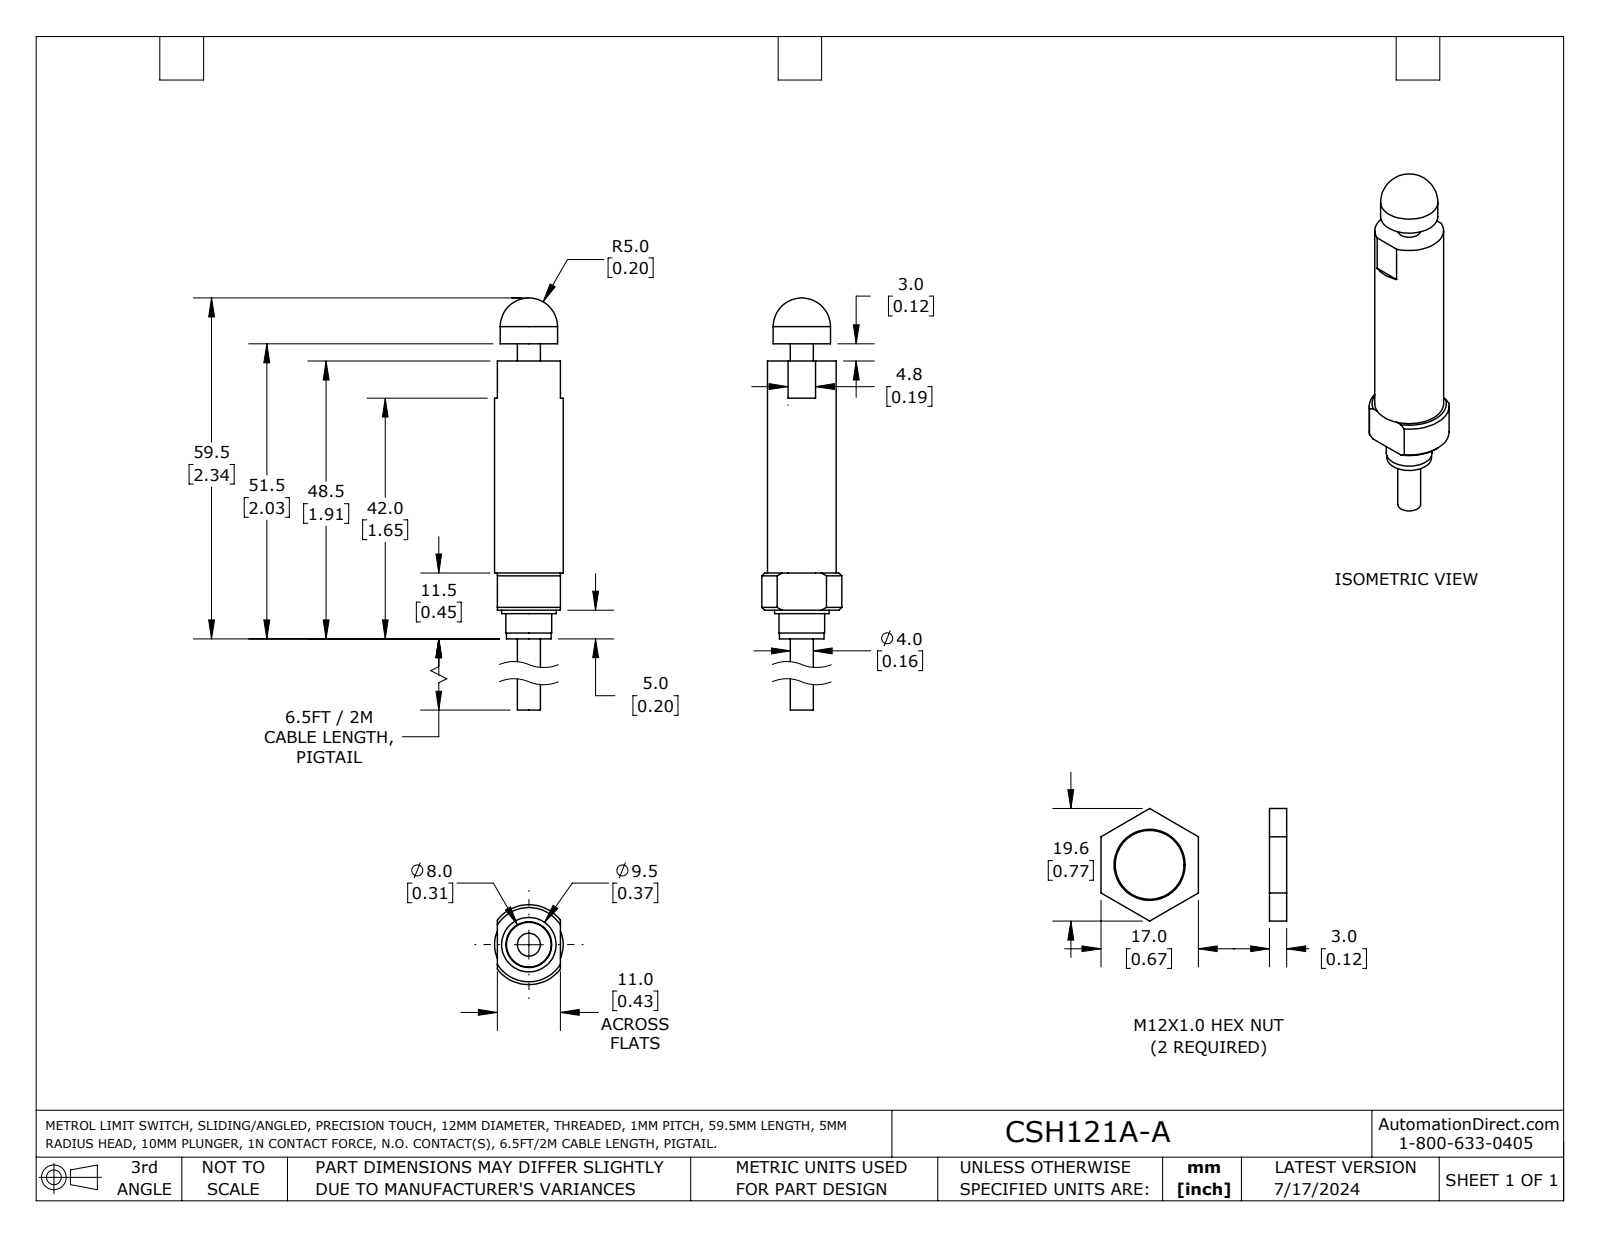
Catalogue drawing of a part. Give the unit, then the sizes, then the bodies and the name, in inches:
Units: inches
Overall size (bounding box): 2.736 × 0.549 × 0.472
Round bosses / shafts (diameter × count): ⌀0.472 ×1, ⌀0.394 ×1, ⌀0.374 ×1, ⌀0.315 ×1, ⌀0.307 ×1, ⌀0.157 ×1
Partial cylindrical surfaces — rounded edges, fillets, slot ends (radius × count): R0.275 ×1
Main face-to-face distances: 0.433, 0.118, 1.713, 1.831, 0.197, 1.909, 2.028, 0.173, 0.024, 1.736
Volume: 0.364 in³ · Surface area: 3.917 in²
Bodies: 1 solid, 31 faces (15 planar, 9 cylindrical, 7 other)
Part name (STEP PRODUCT): CSH121A-A
STEP written by: SolidWorks 2023 (AUTOMOTIVE_DESIGN)
